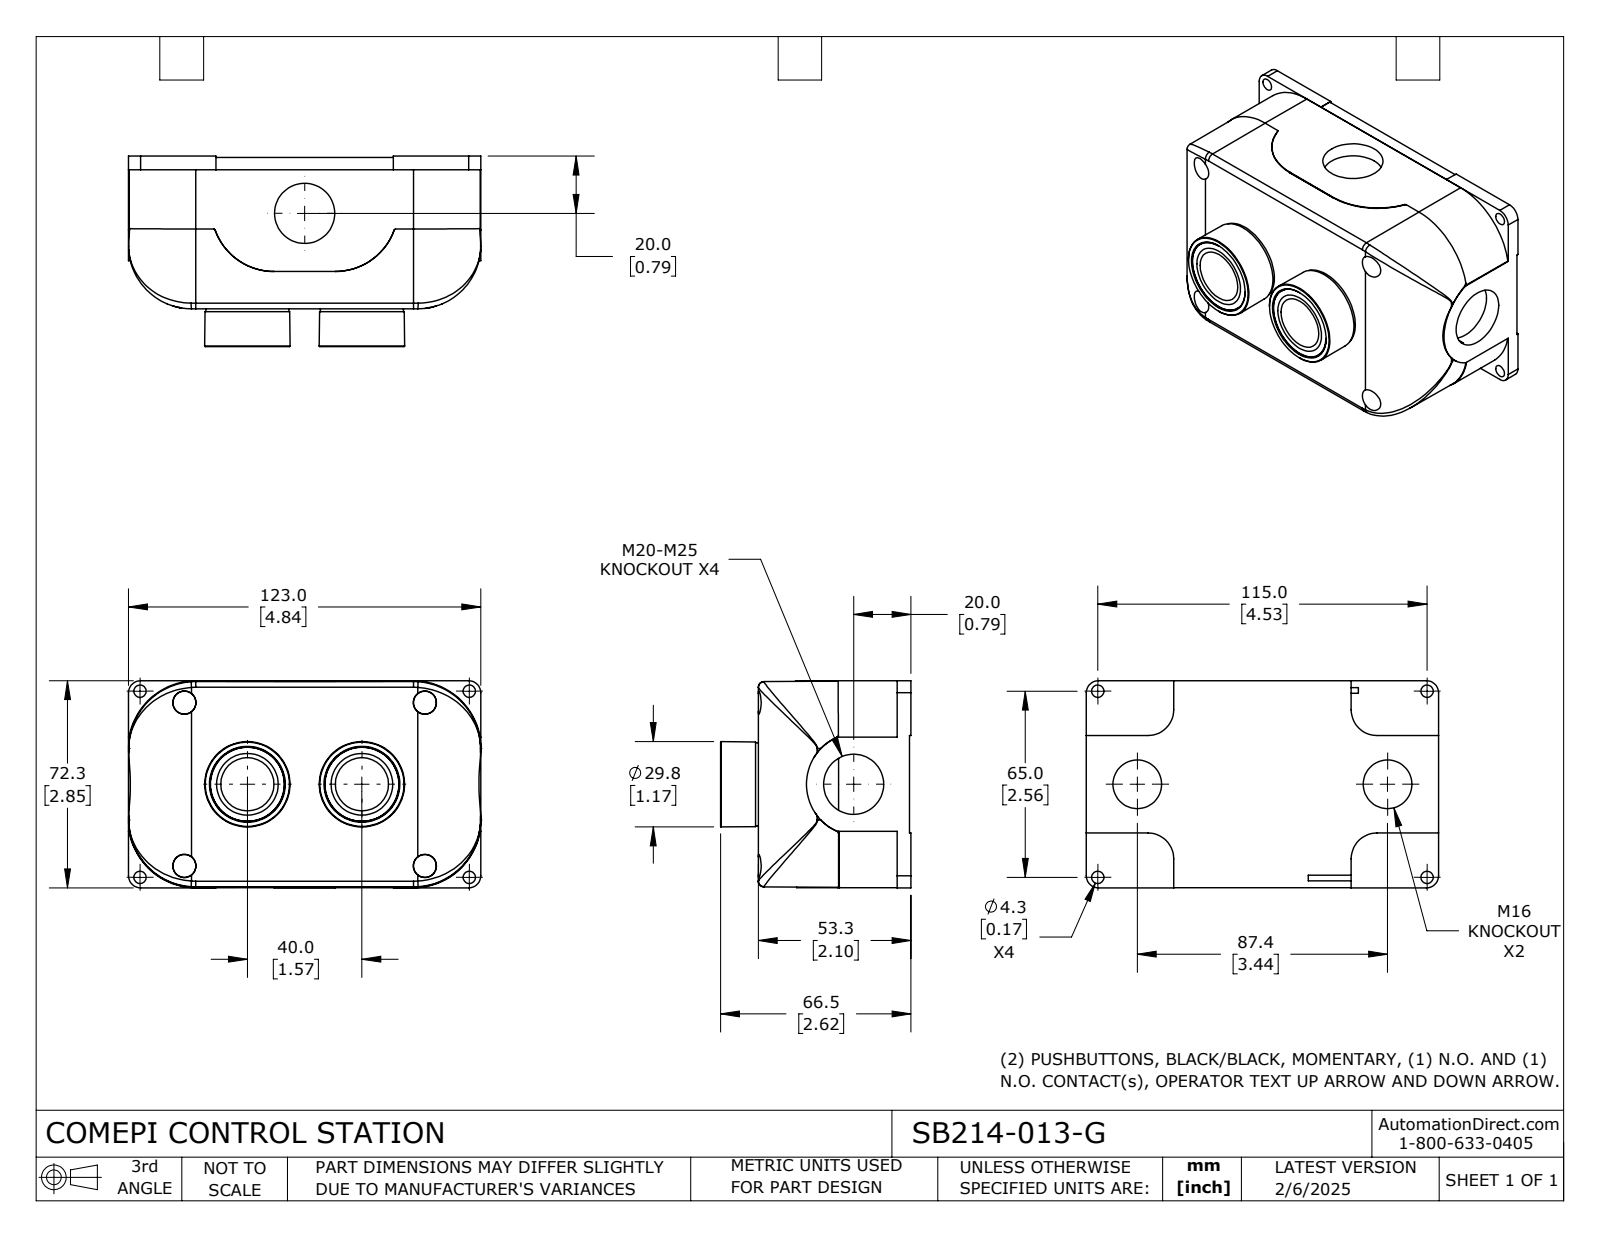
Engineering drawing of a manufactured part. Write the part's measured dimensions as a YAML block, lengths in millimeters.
part_name: "SB214-013-G"
step_written_by: "SolidWorks 2024 (CONFIG_CONTROL_DESIGN)"
units: millimeters
bodies: {solids: 8, faces: 427, planar: 185, cylindrical: 106, other: 136}
overall_size: [123, 72.3, 66.5]
volume: 264000
surface_area: 79810
round_holes:
  - {diameter: 4.3, count: 4}
  - {diameter: 13.5, count: 2}
  - {diameter: 17, count: 2}
  - {diameter: 21, count: 2}
  - {diameter: 21.7, count: 2}
round_bosses_or_shafts:
  - {diameter: 29, count: 2}
  - {diameter: 25.8, count: 2}
  - {diameter: 19, count: 2}
  - {diameter: 16, count: 2}
  - {diameter: 15.6, count: 2}
partial_cylinders:
  - {radius: 0.3, count: 4}
  - {radius: 0.9, count: 4}
  - {radius: 2, count: 4}
  - {radius: 4, count: 4}
  - {radius: 9, count: 4}
  - {radius: 9.7, count: 4}
  - {radius: 22, count: 4}
  - {radius: 23.6, count: 4}
face_to_face_distances: [2.5, 52.8, 50.3, 3, 28, 24.8, 22.3, 53.3, 0.5, 66.5]
hole_center_spacings: [35.3, 49.6, 84, 106.3, 23.7, 63.7, 65, 115]
